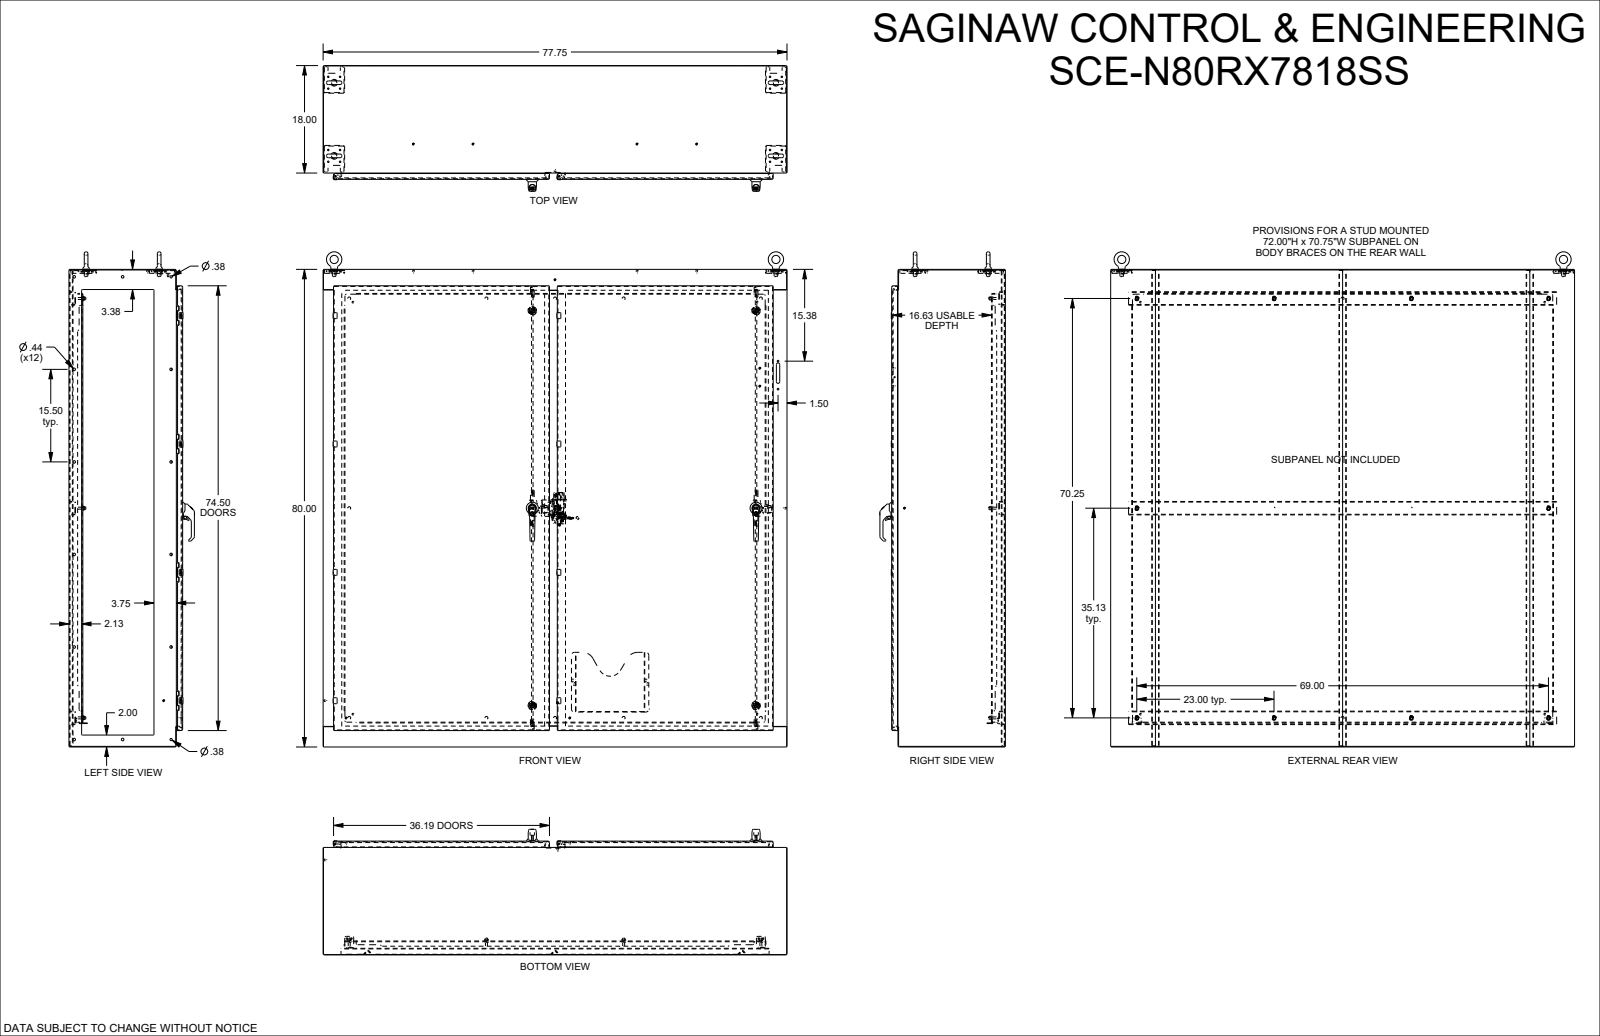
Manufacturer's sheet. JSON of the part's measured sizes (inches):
{"part_name": "SCE-N80RX7818", "step_written_by": "SolidWorks 2023 (AUTOMOTIVE_DESIGN)", "units": "inches", "bodies": {"solids": 50, "faces": 7538, "planar": 3081, "cylindrical": 2573, "other": 1884}, "overall_size": [82.945, 77.75, 21.046], "volume_in3": 2122, "surface_area_in2": 40342, "round_holes": [[0.25, 22], [0.244, 16], [0.375, 16], [0.44, 14], [0.04, 8], [0.17, 8], [0.205, 8], [0.205, 8], [0.218, 8], [0.256, 4], [0.343, 4], [0.344, 4]], "round_bosses_or_shafts": [[0.17, 24], [0.25, 19], [0.24, 16], [0.196, 10], [1.4, 4], [1.173, 4], [0.6, 4], [0.341, 4]], "partial_cylinders_radius": [[0.03, 215], [0.015, 166], [0.125, 96], [0.04, 59], [0.02, 57], [0.02, 48], [0.039, 46], [0.25, 43]], "face_to_face_distances": [0.104, 18.954, 18.85, 19.058, 79.896, 17.896, 1.058, 17.792, 1.162, 80], "hole_center_spacings": [1.979, 37.5, 1.4, 21.5, 12.25, 15.5, 22.457, 2.799]}
